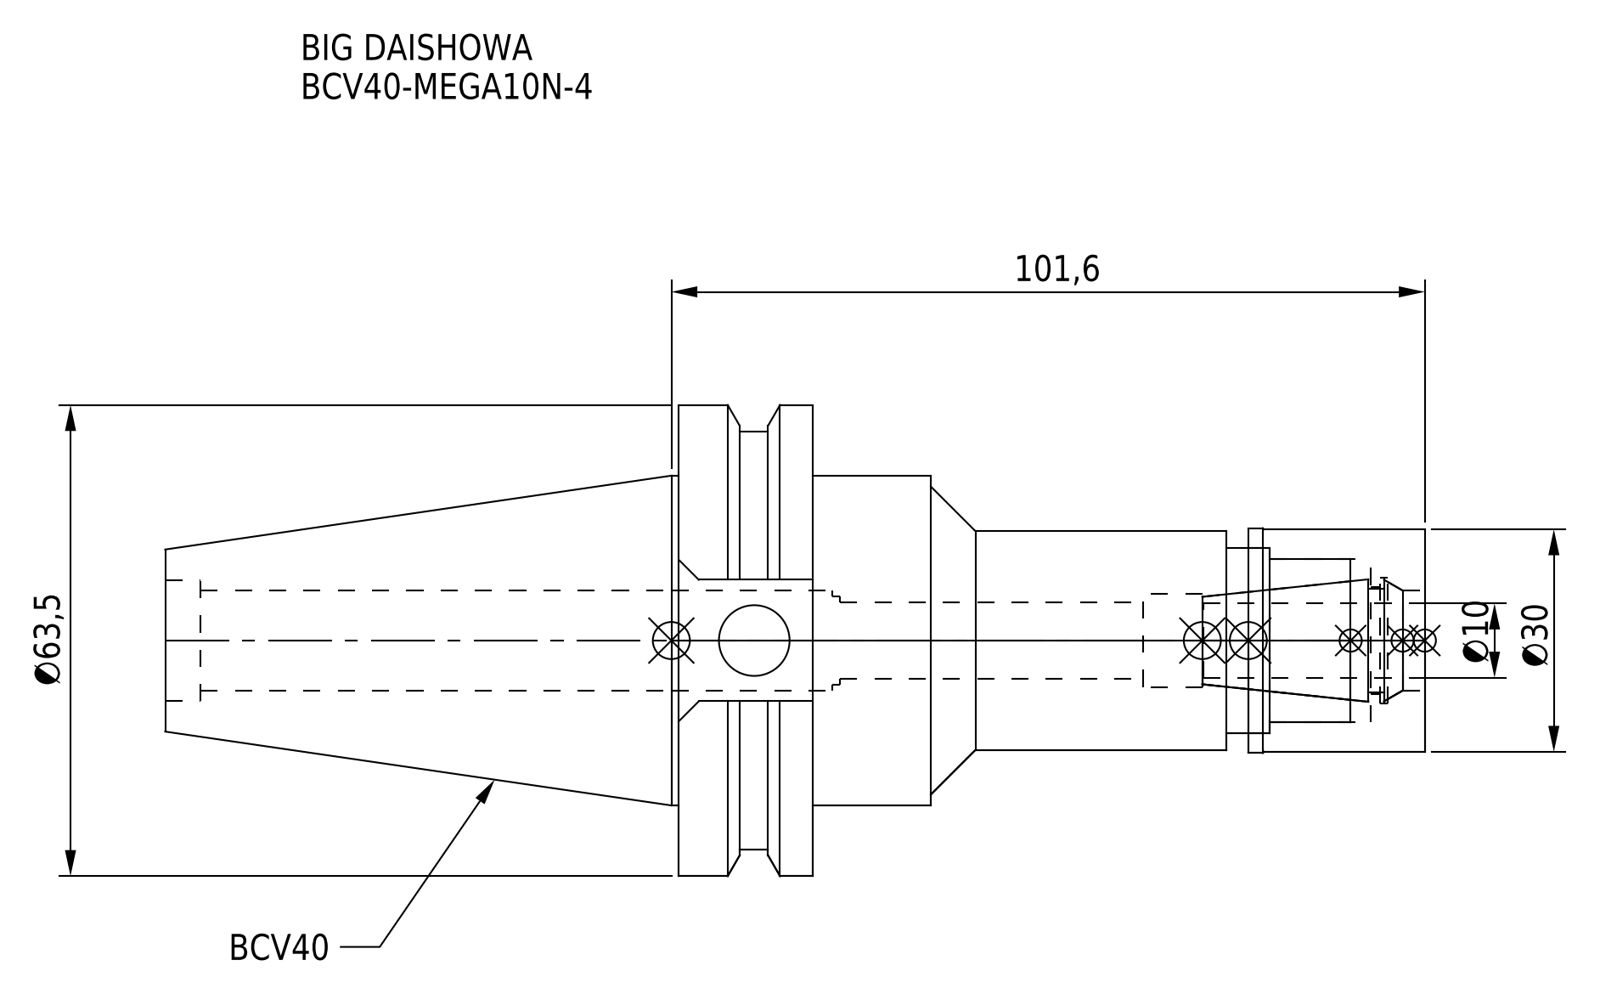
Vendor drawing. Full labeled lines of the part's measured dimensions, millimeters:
Part name (STEP PRODUCT): MGN10_1.stp; DXF_TEMP_ASSY_ASM_4_ASM.stp; BCV40-MEGA10N-4-100-FreeParts; BCV40-MEGA10N-4 (+3 more)
STEP written by: SolidWorks 2019 (CONFIG_CONTROL_DESIGN)
Units: millimetres
Bodies: 2 solids, 91 faces (33 planar, 44 cylindrical, 14 other)
Overall size (bounding box): 169.85 × 63.5 × 61.35
Volume: 165 738 mm³ · Surface area: 35 021 mm²
Round holes (diameter × count): ⌀9.53 ×1, ⌀10.4 ×1, ⌀12 ×1, ⌀12.5 ×1, ⌀13.5 ×1, ⌀13.6 ×1, ⌀14.5 ×1, ⌀16.32 ×1, ⌀17 ×1, ⌀22 ×1, ⌀25 ×1
Round bosses / shafts (diameter × count): ⌀63.5 ×1, ⌀56.36 ×1, ⌀44.45 ×1, ⌀30.3 ×1, ⌀30 ×1, ⌀29.5 ×1
Main face-to-face distances: 18.05, 82.55, 100.6, 169.85, 87.3, 69.25, 47.55, 23.8, 58.75, 76.8
